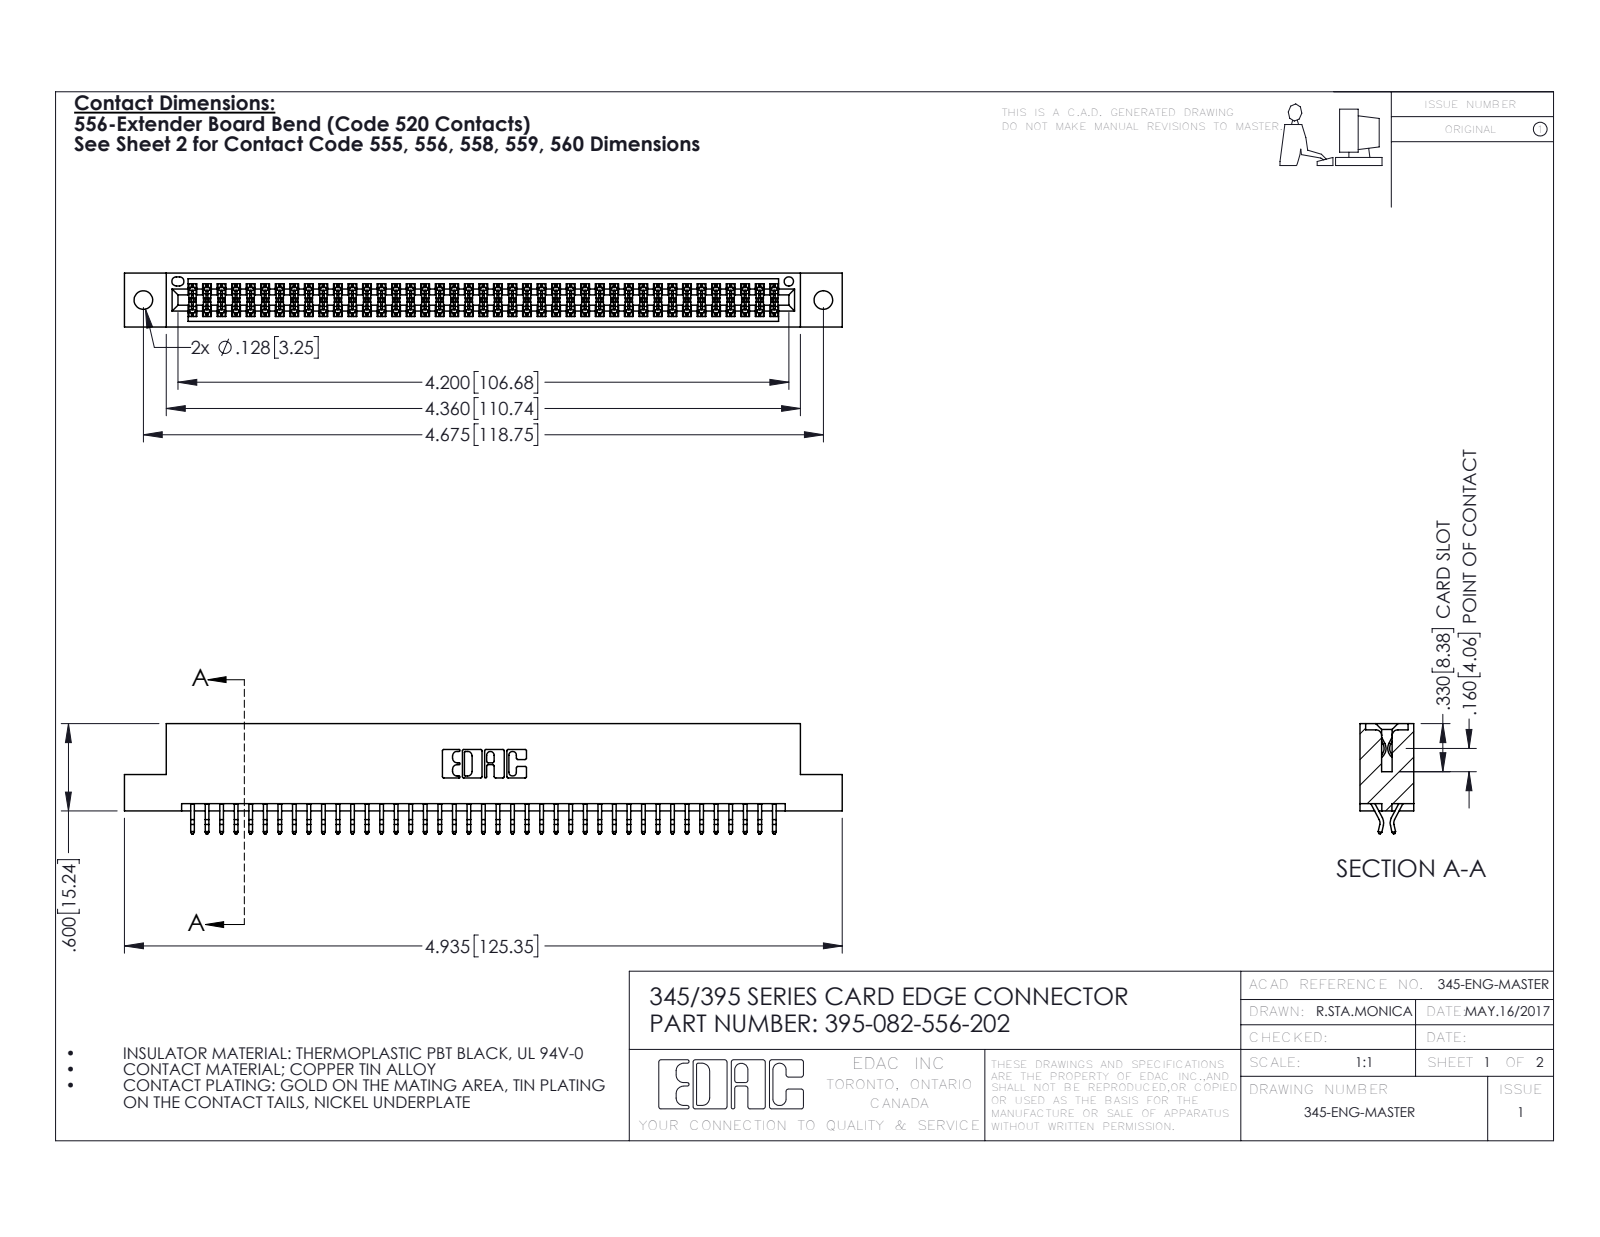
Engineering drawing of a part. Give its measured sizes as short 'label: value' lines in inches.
name: 345 Part_Flush Mounting Lugs - 0.128 Dia; 395-082-556-202; 345-292-001_556 Tail
written by: SolidWorks 2016 (CONFIG_CONTROL_DESIGN)
unit: in
bodies: 83 solids, 4718 faces (3114 planar, 1604 cylindrical, 0 other)
size: 4.935 × 0.757 × 0.37
volume: 0.74 in³; area: 27.22 in²
holes: 2× ⌀0.128, 1× ⌀0.064
rounds: 123× R0.006, 22× R0.01, 6× R0.007, 6× R0.031, 3× R0.026, 2× R0.01, 2× R0.014, 2× R0.019
face distances: 0.298, 0.072, 0.37, 0.2, 0.025, 0.098, 0.272, 0.225, 0.175, 0.149
hole spacings: 0.27, 4.439, 4.675
